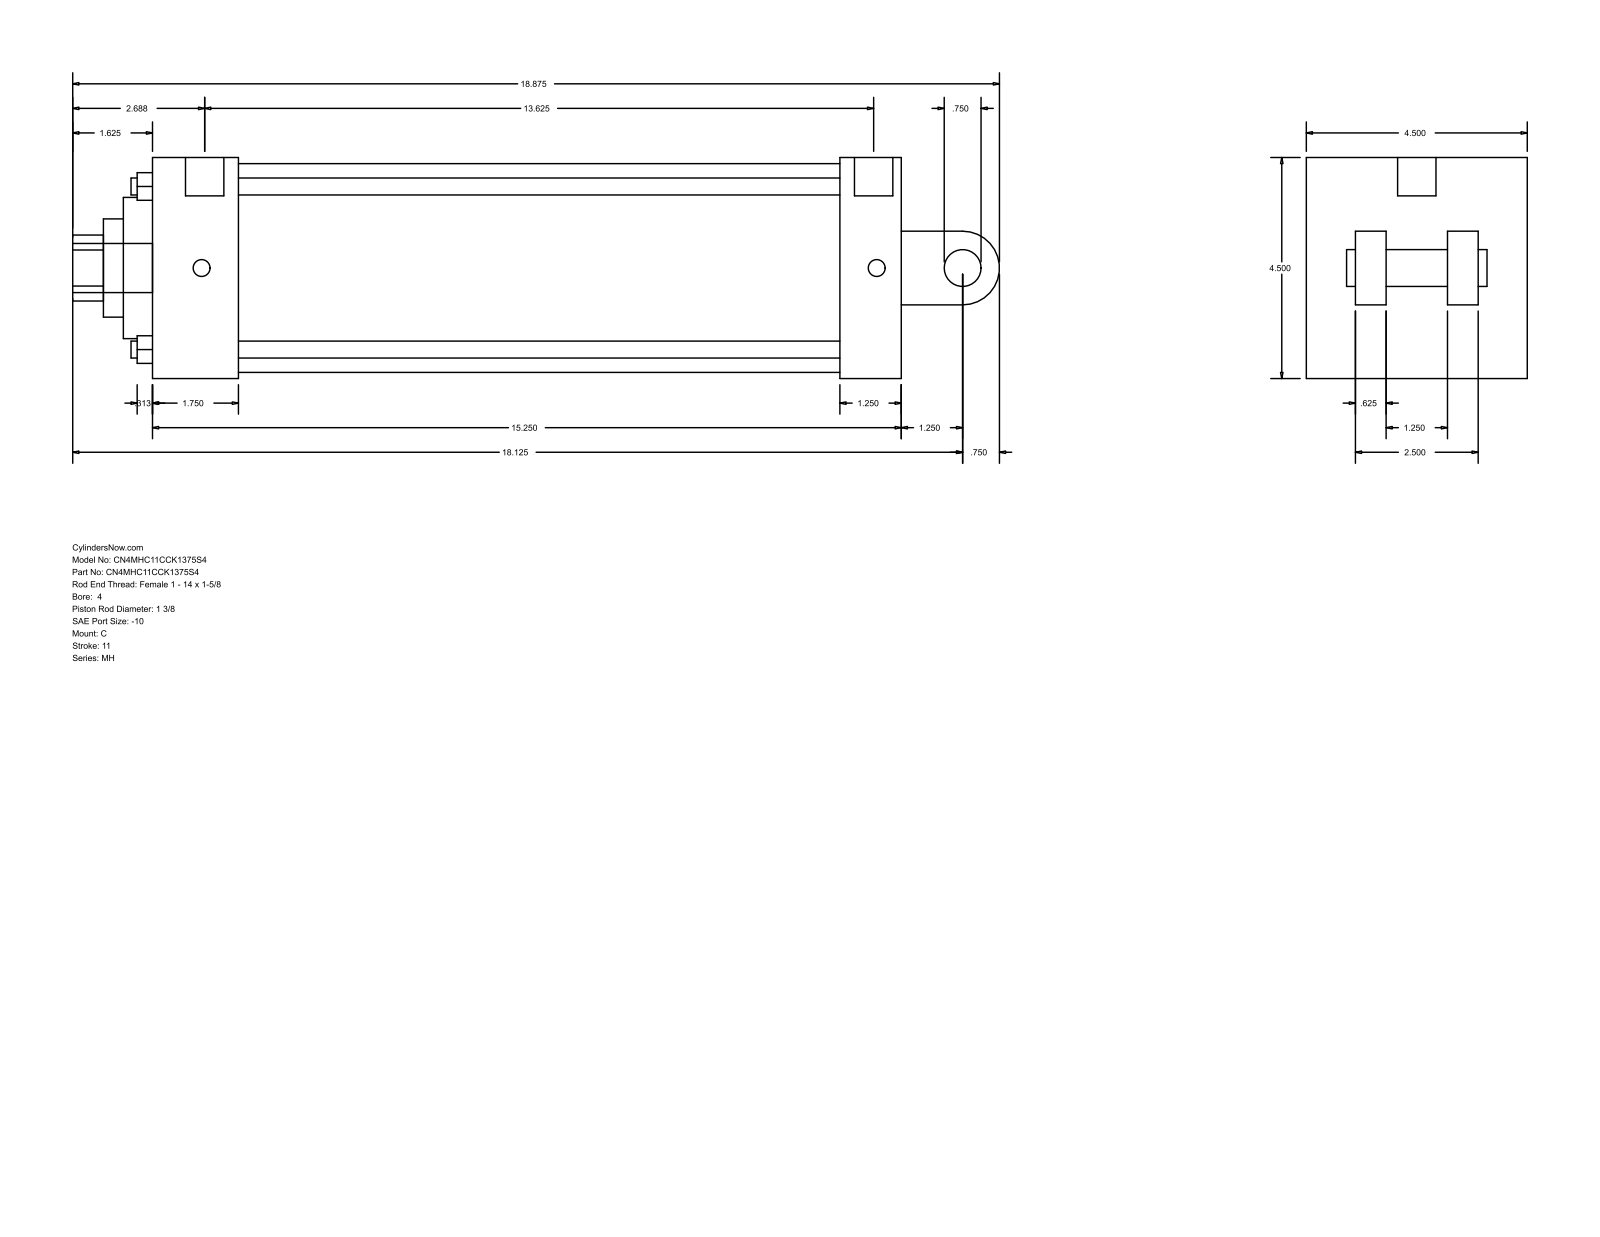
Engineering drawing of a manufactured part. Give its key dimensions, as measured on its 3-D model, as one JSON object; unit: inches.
{"part_name": "MH_C__0400_1.375", "step_written_by": "GSSL Pune (CONFIG_CONTROL_DESIGN)", "units": "inches", "bodies": {"solids": 0, "faces": 101, "planar": 71, "cylindrical": 30, "other": 0}, "overall_size": [18.875, 4.5, 4.5], "round_holes": [[0.345, 4], [0.344, 2], [0.781, 1], [1.375, 1], [2, 1], [2.875, 1], [4.25, 1]], "round_bosses_or_shafts": [[0.344, 2], [1, 1], [0.781, 1], [0.75, 1]], "partial_cylinders_radius": [[0.672, 1], [0.75, 1]], "face_to_face_distances": [4.5, 15.25, 1.75, 14, 12.25, 13.5, 1.25, 2.875, 1.625, 1.5], "hole_center_spacings": [2.347, 3.32, 4.695, 0.063]}
